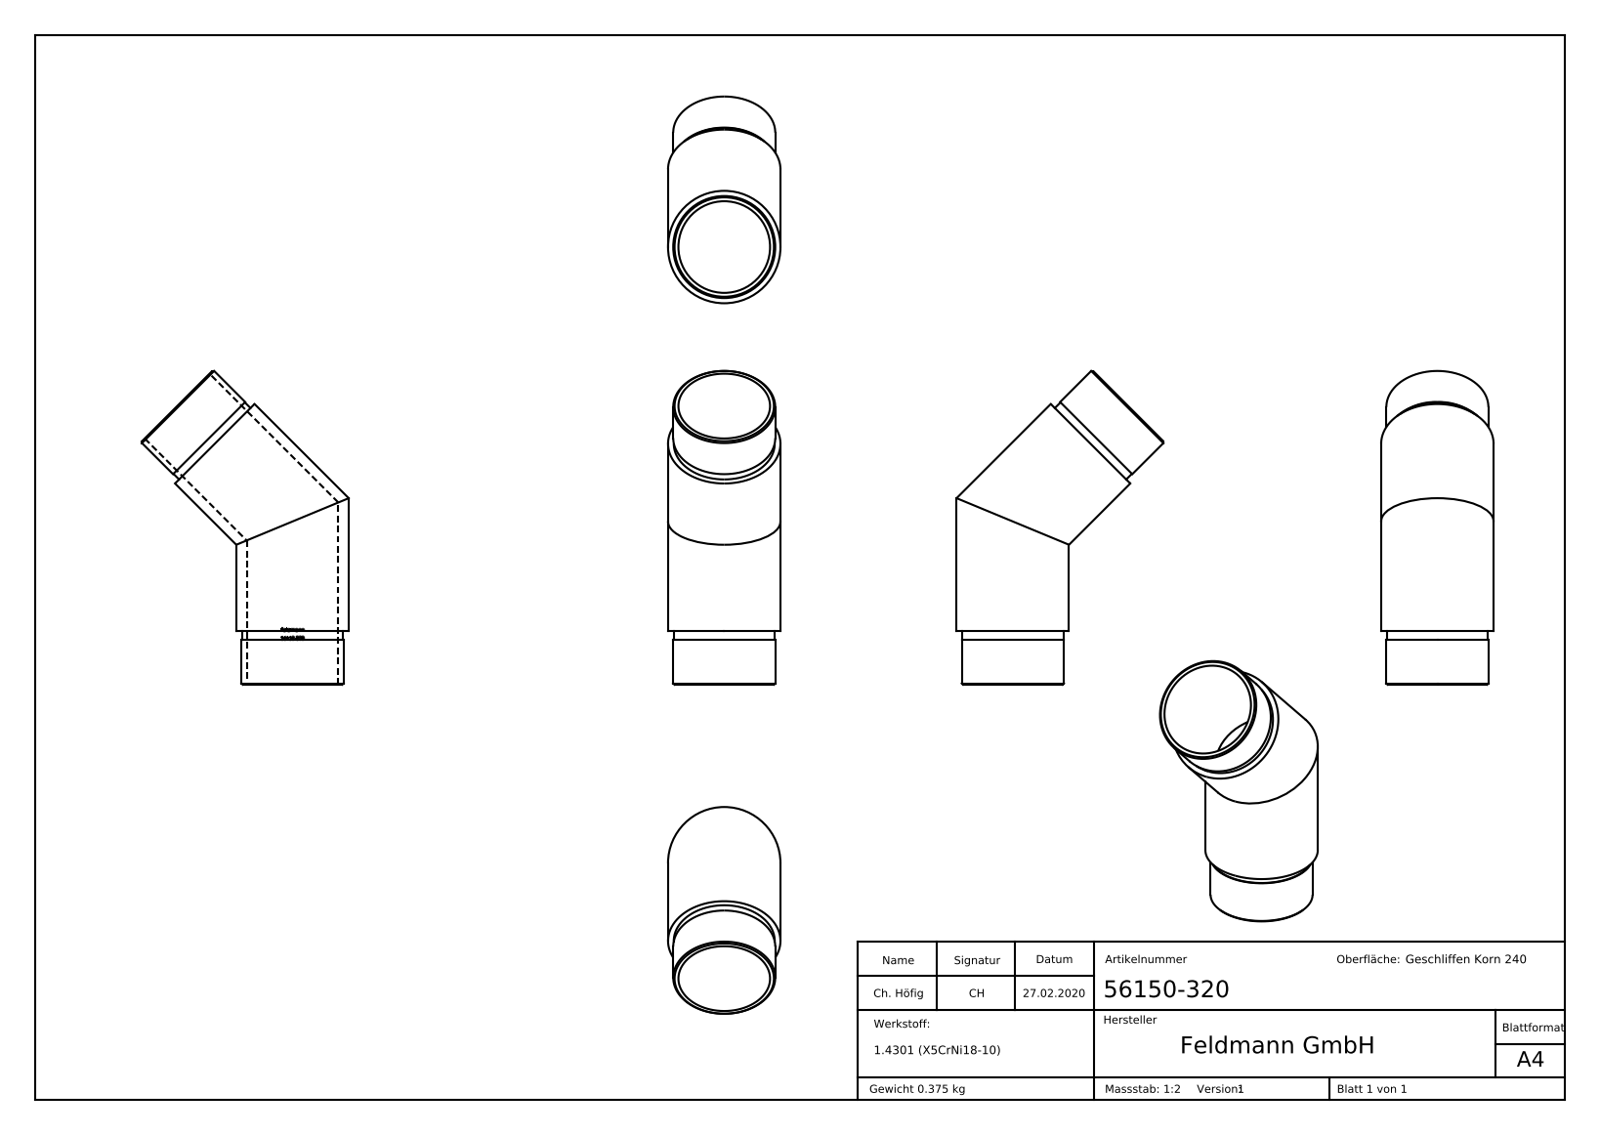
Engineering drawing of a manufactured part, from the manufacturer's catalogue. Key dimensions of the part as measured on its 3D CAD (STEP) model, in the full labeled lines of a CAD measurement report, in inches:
Part name (STEP PRODUCT): 56150-320
STEP written by: SolidWorks 2015 (CONFIG_CONTROL_DESIGN)
Units: inches
Bodies: 1 solid, 238 faces (94 planar, 31 cylindrical, 113 other)
Overall size (bounding box): 4.637 × 3.056 × 1.661
Volume: 2.896 in³ · Surface area: 46.44 in²
Round holes (diameter × count): ⌀1.354 ×2
Round bosses / shafts (diameter × count): ⌀1.661 ×2, ⌀1.508 ×2, ⌀1.492 ×2
Partial cylindrical surfaces — rounded edges, fillets, slot ends (radius × count): R0.681 ×1
Main face-to-face distances: 0.787, 0.669, 0.118, 0.015, 0.044, 0.05, 0.117, 0.052, 0.167, 0.08
